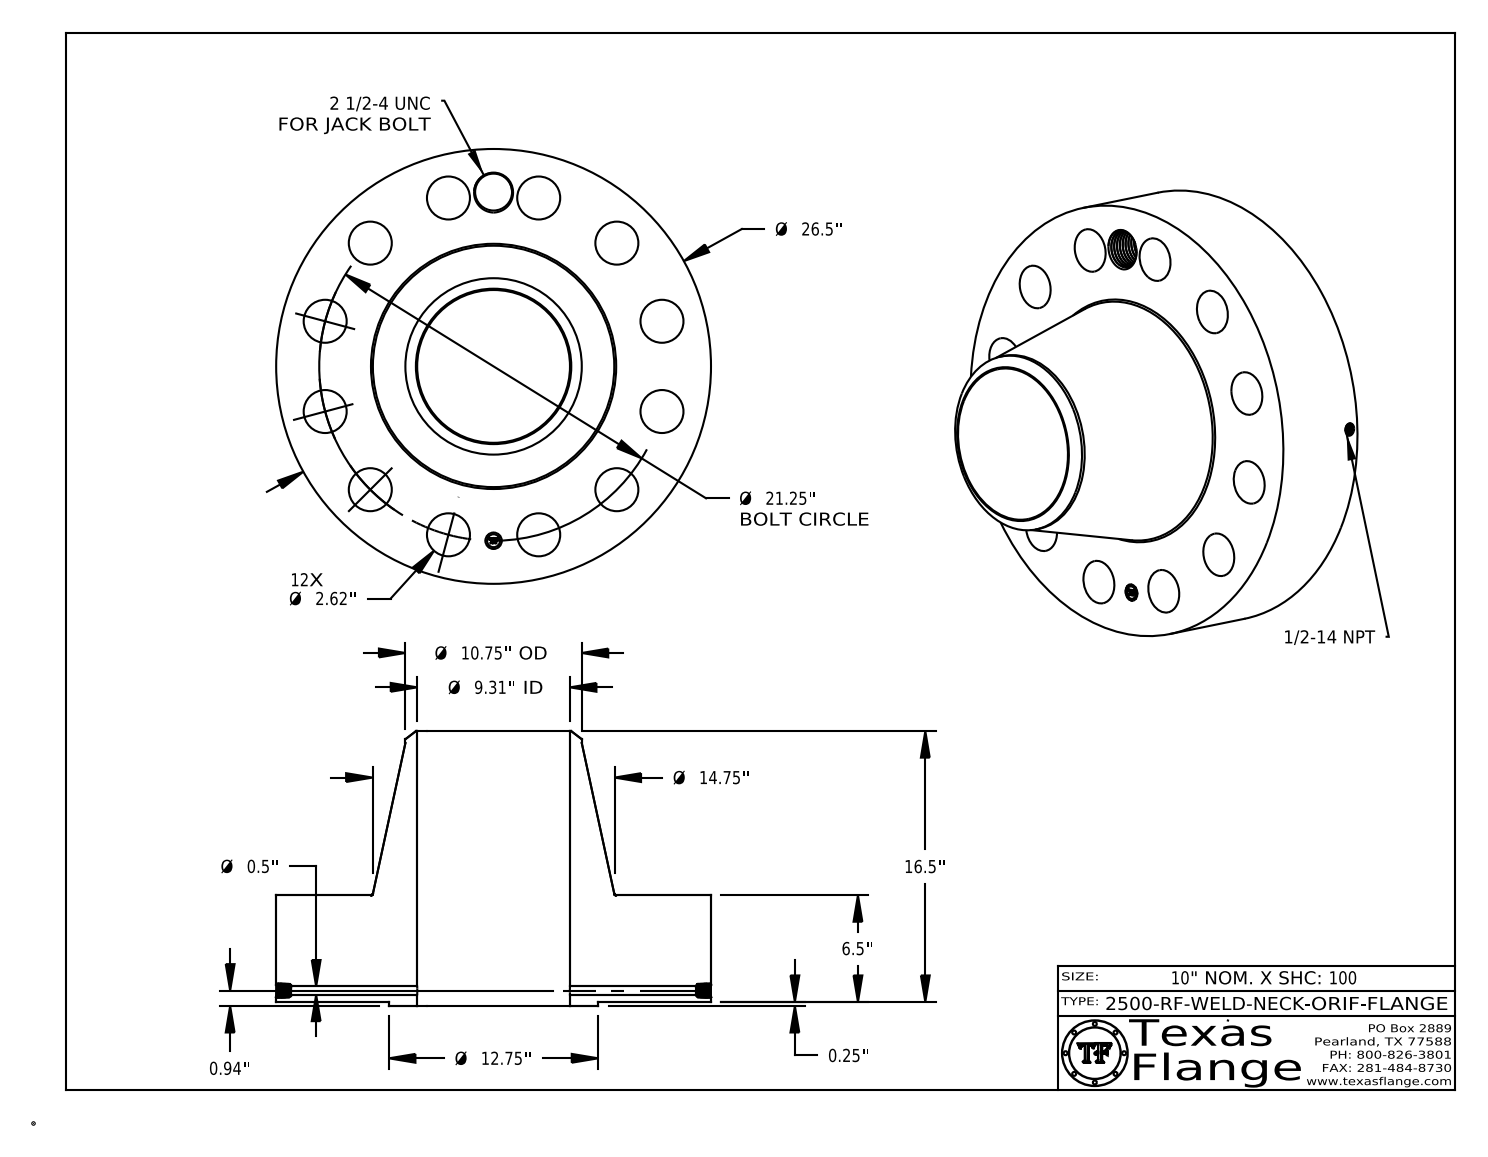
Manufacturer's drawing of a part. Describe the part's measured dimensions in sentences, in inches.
The part is named "2500-RF-WELD-NECK". Its 3-D file was written by "CATIA V5 STEP AP214 (AUTOMOTIVE_DESIGN)". It is 1 solid with 843 faces: 369 planar, 124 cylindrical and 350 other. Overall it measures 26.5 by 26.5 by 16.75 inches. Its volume is 3 278 cubic inches and its surface area 2 923 square inches. Round holes: 12 of diameter 2.62, 1 of diameter 0.5, 1 of diameter 0.672, 1 of diameter 1, 1 of diameter 2.25, 1 of diameter 9.312. Round bosses or shafts: 8 of diameter 0.061, 1 of diameter 26.5, 1 of diameter 12.75, 1 of diameter 10.75, 1 of diameter 0.788. The main face-to-face distances are 6.5, 0.25, 6.75, 16.75, 16.5, 10, 0.015, 6.735, 6.485, 10.015. The hole center spacings are 10.625, 5.5, 15.026, 18.403, 20.526, 10.625, 21.25, 2.774.
